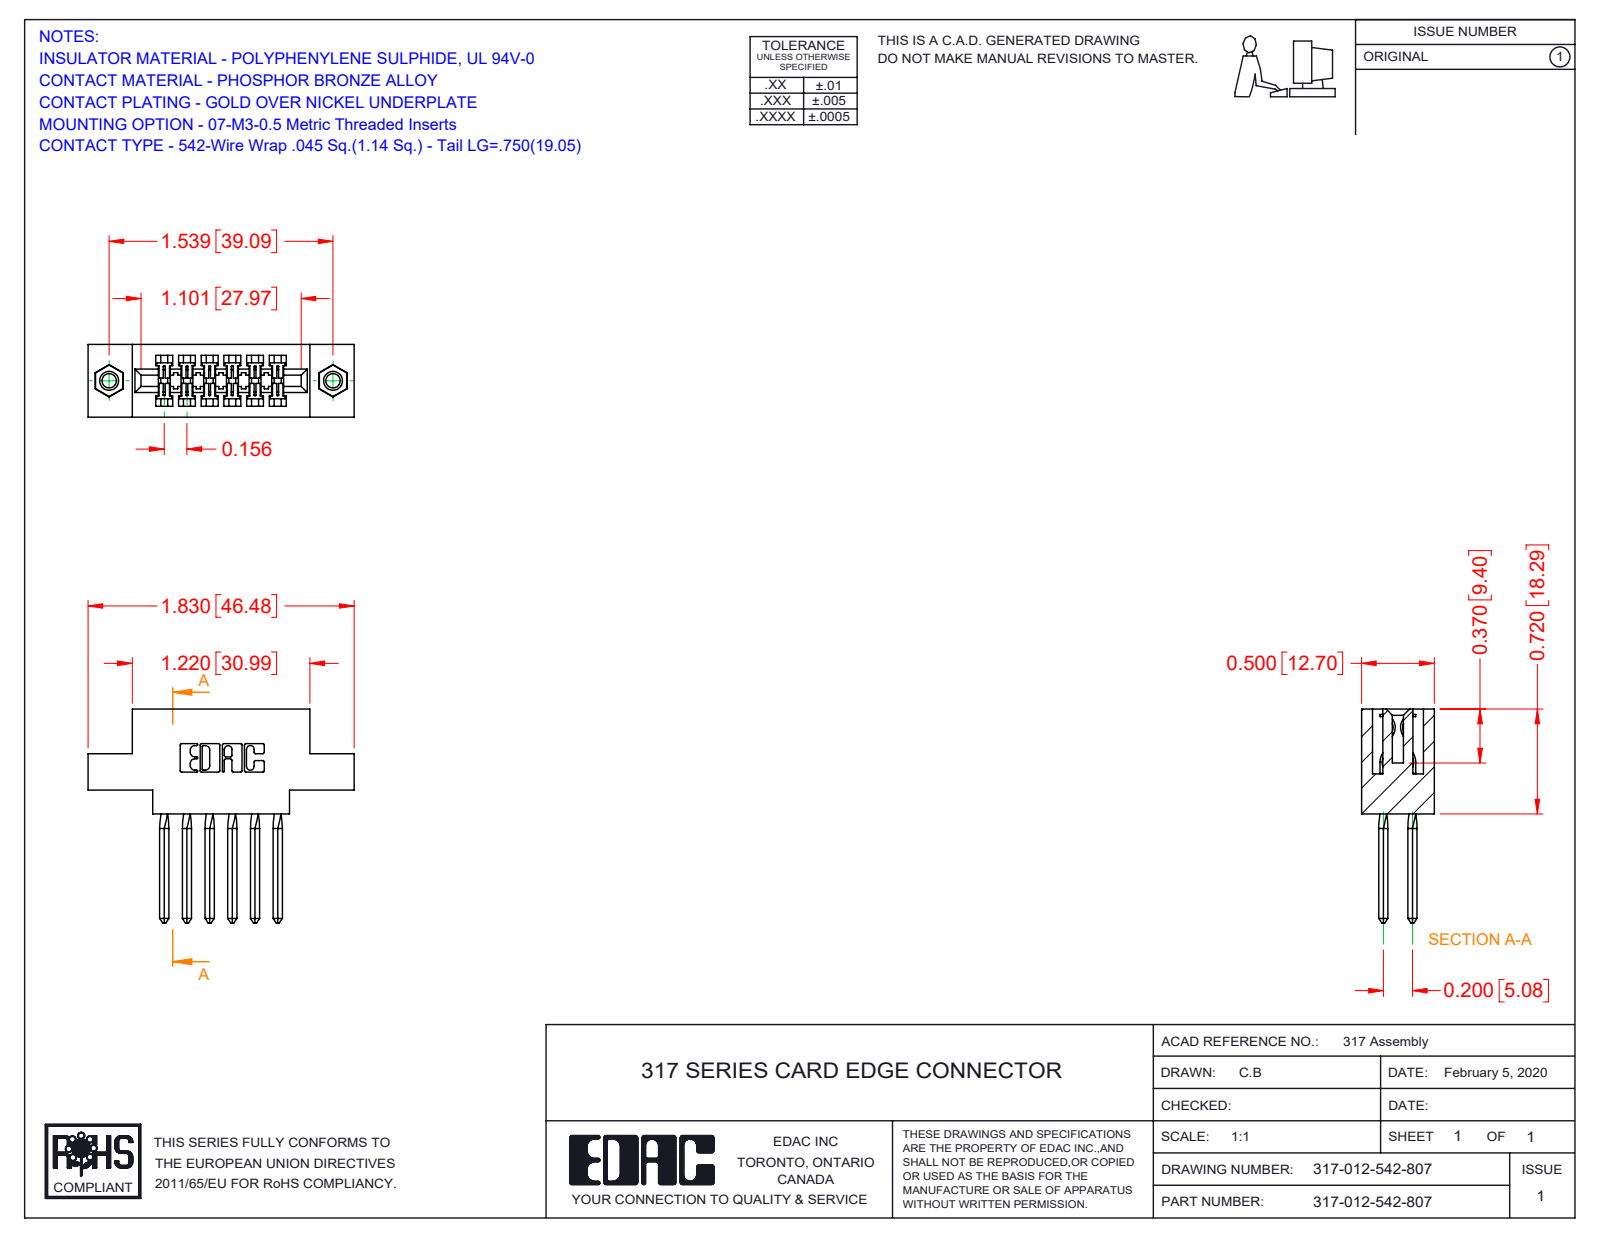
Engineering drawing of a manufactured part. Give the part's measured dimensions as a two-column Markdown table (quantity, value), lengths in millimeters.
| quantity | value |
| --- | --- |
| part name | 317-012-542-807; 317-290-003_542; 317 Part_.156 Dia - TI; 345-250-001_345-250-005-103 |
| STEP written by | SolidWorks 2016 (CONFIG_CONTROL_DESIGN) |
| units | millimeters |
| bodies | 15 solids, 846 faces (642 planar, 140 cylindrical, 64 other) |
| overall size | 46.5 × 37.3 × 12.7 |
| volume | 6 460 mm³ |
| surface area | 7 865 mm² |
| round holes (diameter × count) | 2.5 × 2, 3.2 × 2, 4 × 2 |
| round bosses / shafts (diameter × count) | 3.9 × 2 |
| partial cylindrical surfaces (radius × count) | 0.2 × 24, 0.3 × 22, 0.2 × 6, 0.8 × 6, 0.7 × 3, 1.9 × 2, 2.3 × 2, 2.5 × 2 |
| main face-to-face distances | 12.7, 2.8, 1.9, 10.8, 5.6, 1.7, 2.9, 4, 1.1, 4.1 |
| hole center spacings | 39.1 |
